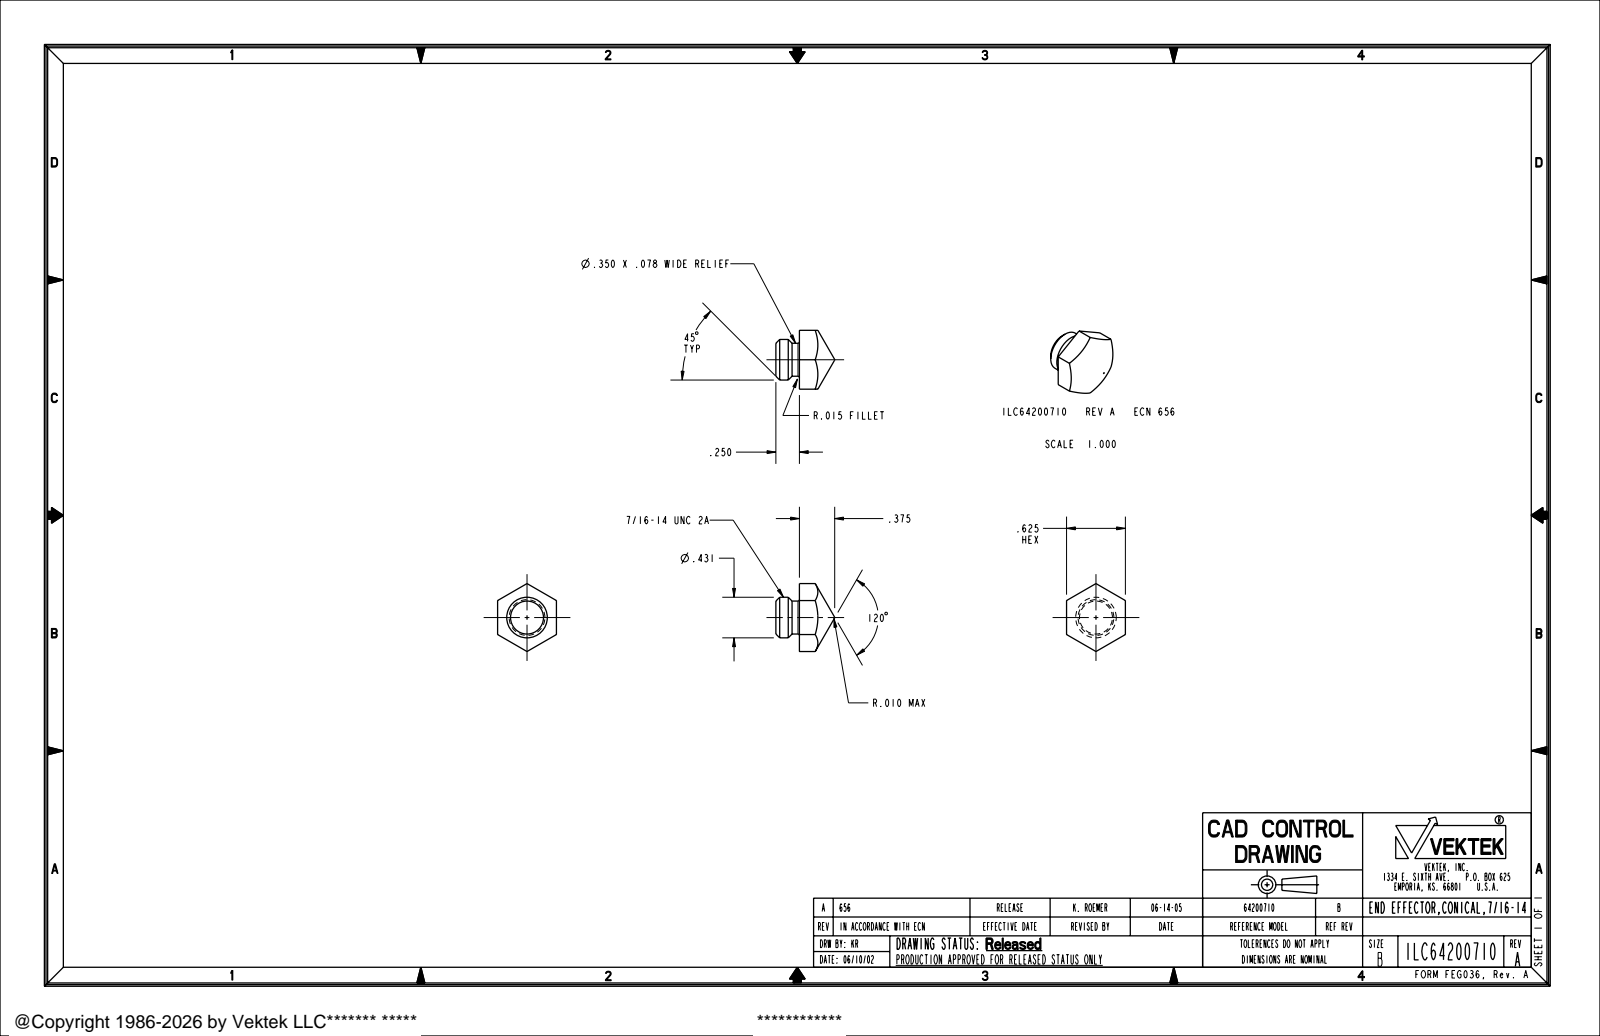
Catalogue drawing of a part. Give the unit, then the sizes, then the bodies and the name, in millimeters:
Units: millimetres
Overall size (bounding box): 18.3 × 15.9 × 15.9
Round bosses / shafts (diameter × count): ⌀10.9 ×1, ⌀8.9 ×1
Main face-to-face distances: 15.9, 6.4
Volume: 1 880 mm³ · Surface area: 952 mm²
Bodies: 1 solid, 22 faces (8 planar, 4 cylindrical, 10 other)
Part name (STEP PRODUCT): ILC64200710
STEP written by: PRO/ENGINEER BY PARAMETRIC TECHNOLOGY CORPORATION, 2004290 (AUTOMOTIVE_DESIGN_CC2)
